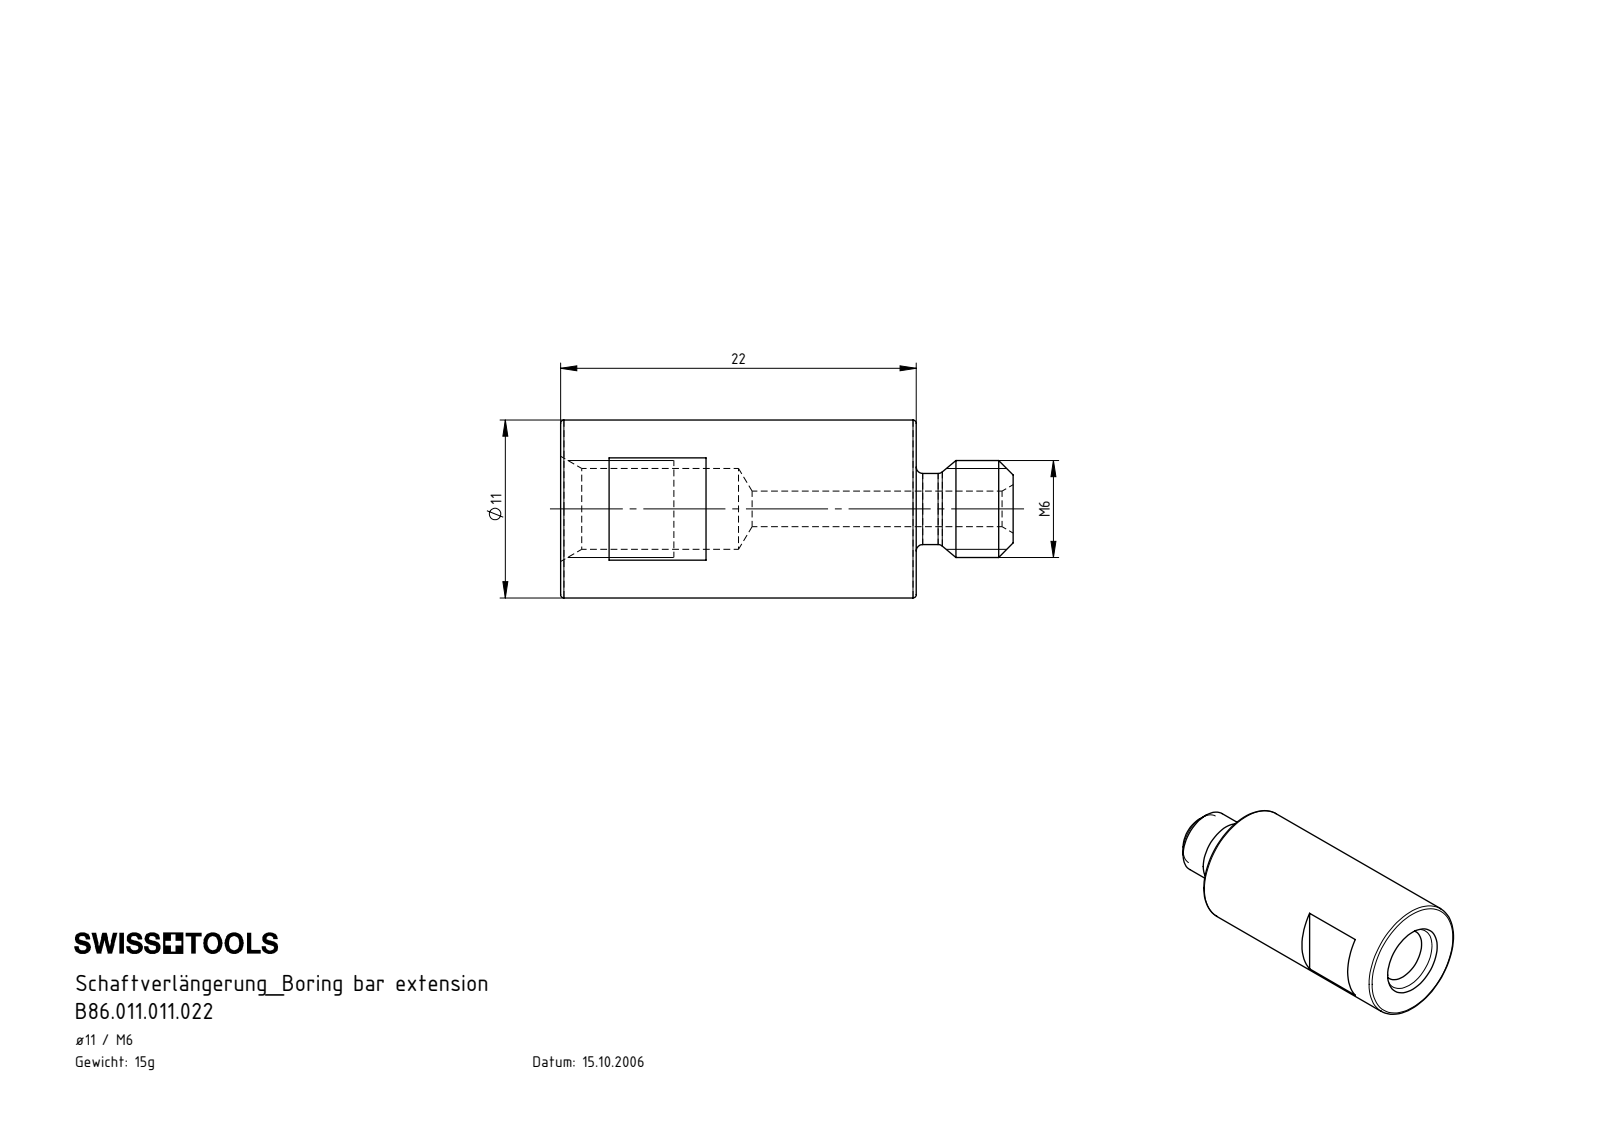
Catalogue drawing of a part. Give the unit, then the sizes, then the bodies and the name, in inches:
Units: inches
Overall size (bounding box): 1.102 × 0.433 × 0.433
Round holes (diameter × count): ⌀0.087 ×1, ⌀0.197 ×1
Round bosses / shafts (diameter × count): ⌀0.433 ×1, ⌀0.236 ×1, ⌀0.173 ×1
Main face-to-face distances: 0.866, 0.354, 0.748, 0.236, 0.118, 0.512, 0.984, 1.102
Volume: 0.115 in³ · Surface area: 2.069 in²
Bodies: 1 solid, 37 faces (9 planar, 10 cylindrical, 18 other)
Part name (STEP PRODUCT): B86.011.011.022
STEP written by: SolidWorks 2022 (CONFIG_CONTROL_DESIGN)
